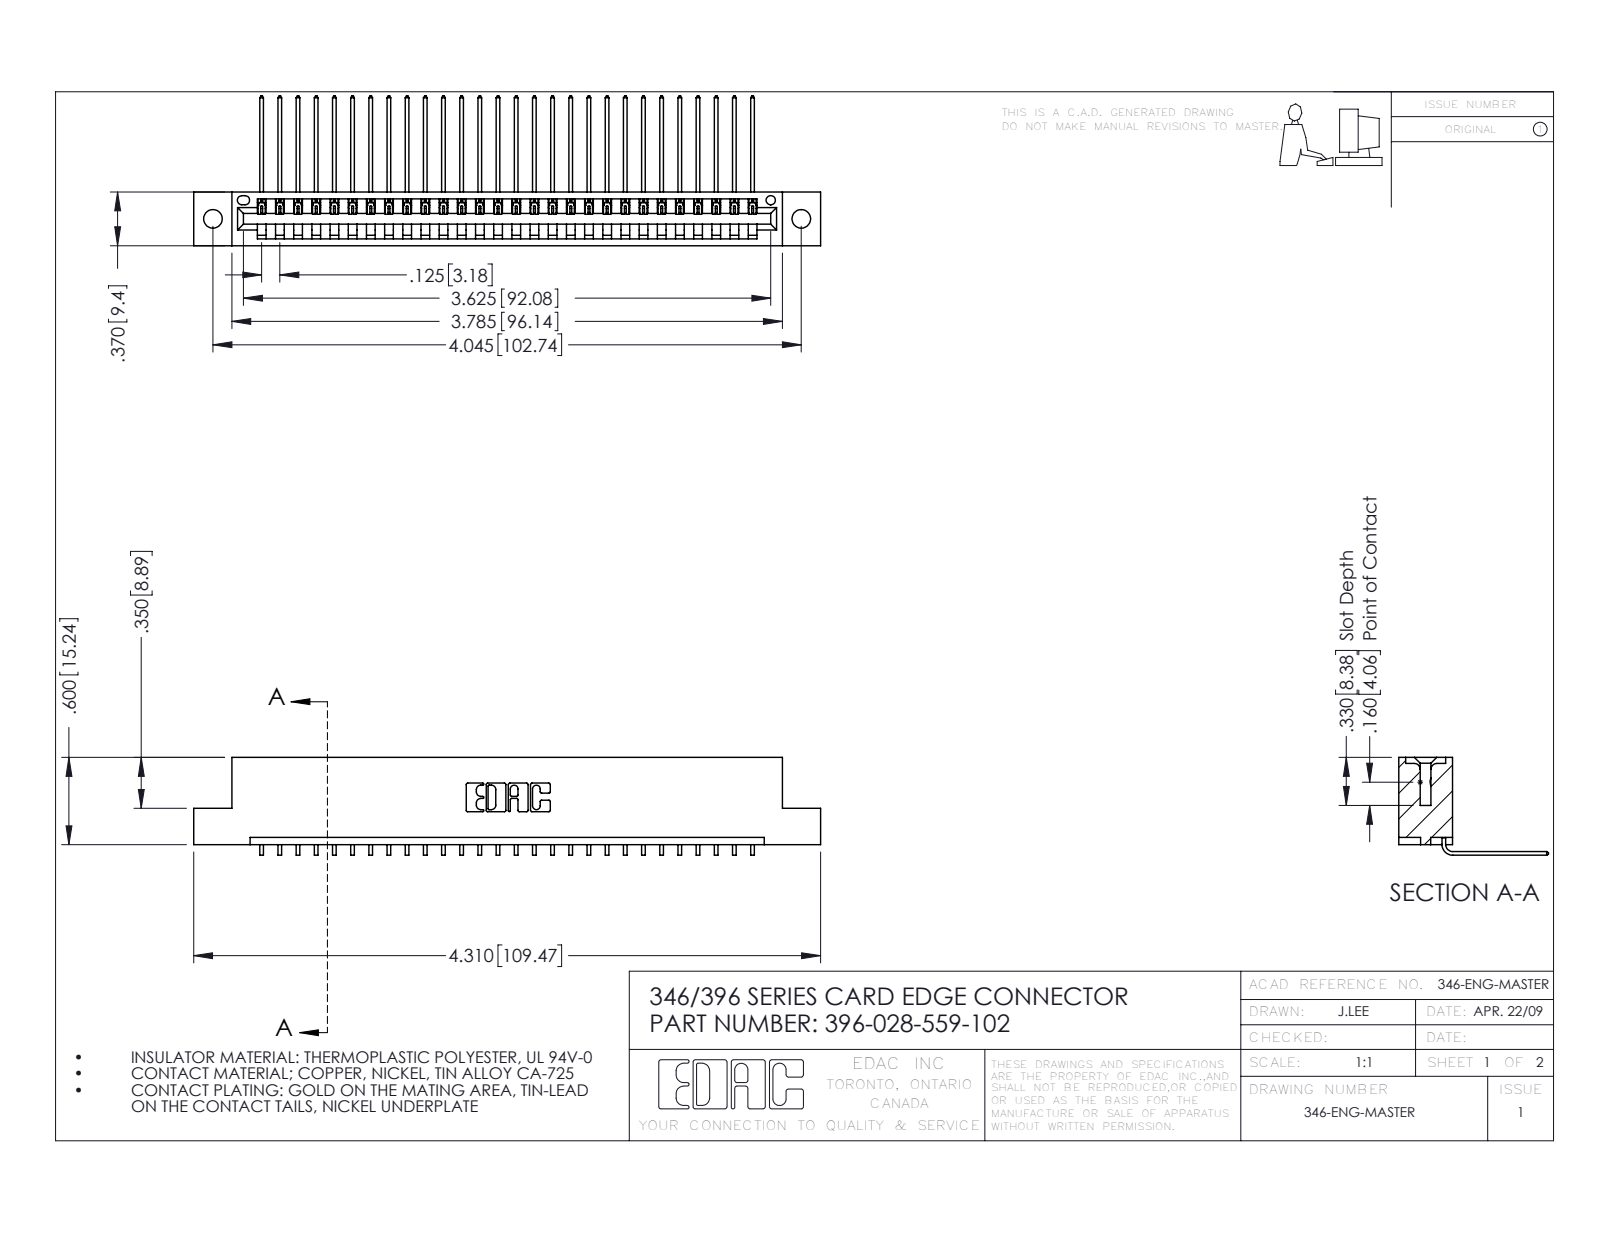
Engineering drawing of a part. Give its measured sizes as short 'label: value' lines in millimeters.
name: 396-028-559-102; 346 Part_Flush Mounting Lugs - 0.128 Dia; 345-292-001_558 559 Tail - 1
written by: SolidWorks 2016 (CONFIG_CONTROL_DESIGN)
unit: mm
bodies: 29 solids, 1802 faces (1252 planar, 550 cylindrical, 0 other)
size: 109.5 × 26.2 × 17.1
volume: 10 400 mm³; area: 13 180 mm²
holes: 2× ⌀3.3, 1× ⌀1.6
rounds: 56× R0.2, 22× R0.3, 6× R0.2, 6× R0.8, 3× R0.7, 2× R0.8, 2× R1, 1× R0.4
face distances: 1.2, 8.2, 9.4, 6.4, 1.8, 0.6, 7.6, 3.8, 5.6, 2.5
hole spacings: 6.2, 97.5, 102.7
